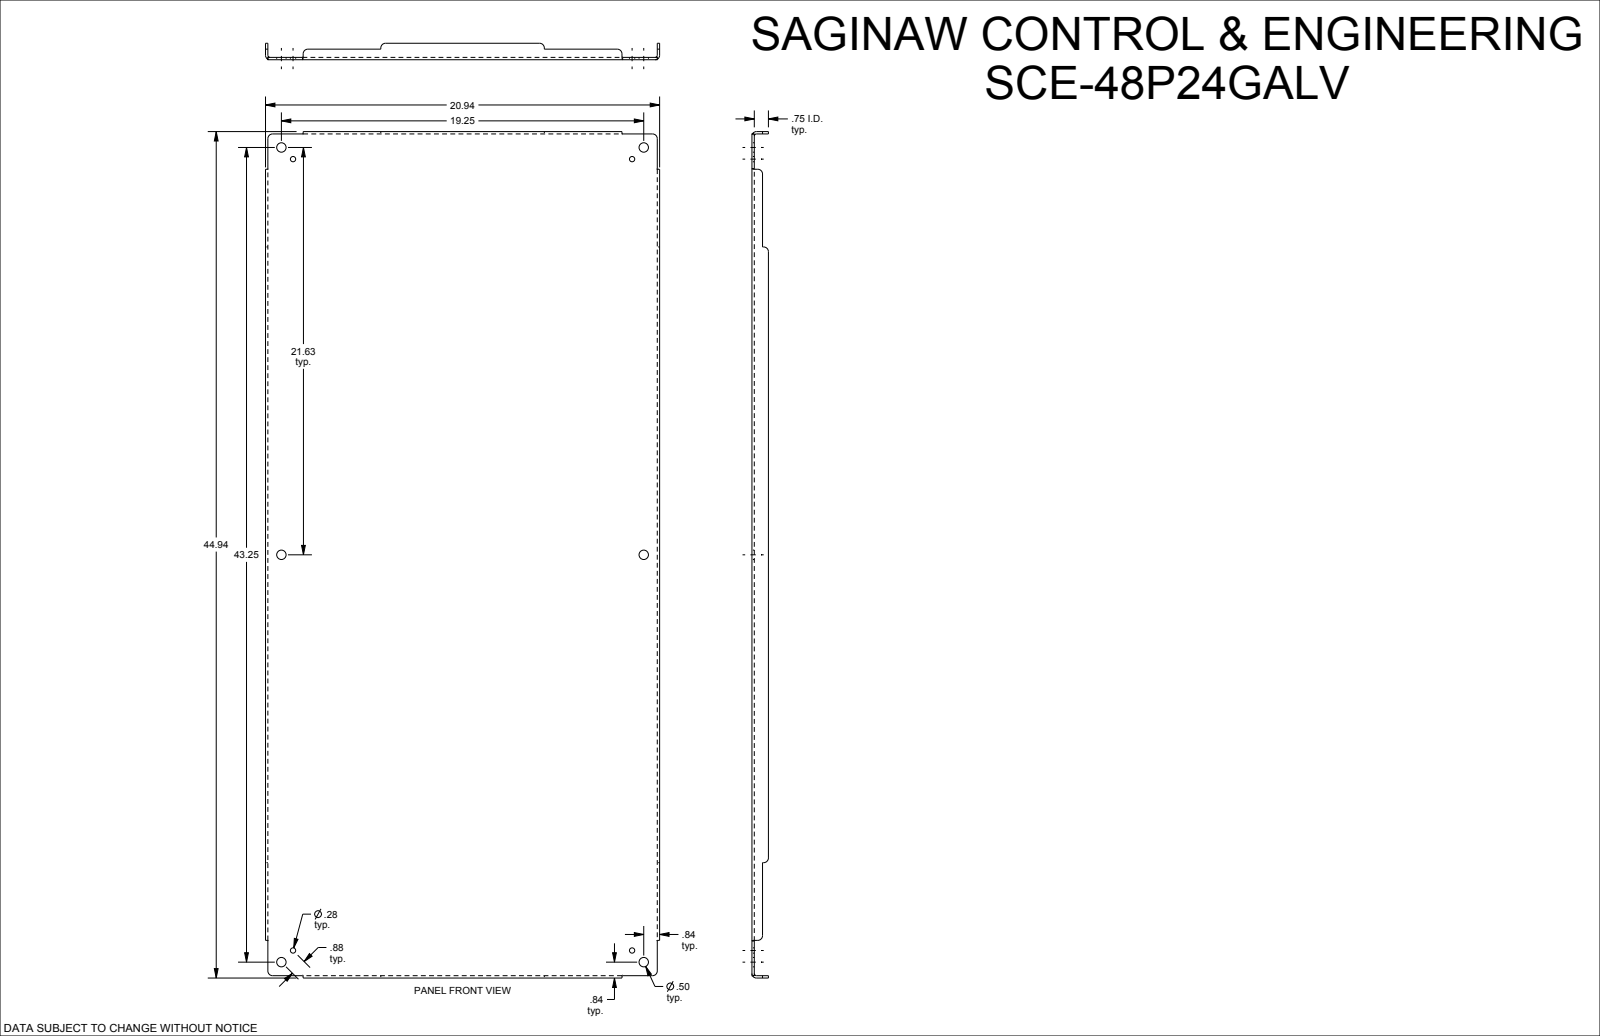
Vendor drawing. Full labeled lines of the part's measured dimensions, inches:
Part name (STEP PRODUCT): SCE-48P24GALV
STEP written by: SolidWorks 2019 (CONFIG_CONTROL_DESIGN)
Units: inches
Bodies: 1 solid, 108 faces (46 planar, 38 cylindrical, 24 other)
Overall size (bounding box): 44.938 × 20.938 × 0.875
Volume: 125.6 in³ · Surface area: 2 029 in²
Round holes (diameter × count): ⌀0.5 ×6, ⌀0.281 ×4
Partial cylindrical surfaces — rounded edges, fillets, slot ends (radius × count): R0.25 ×12, R0.112 ×4, R0.237 ×4
Main face-to-face distances: 0.125, 0.125, 20.813, 20.687, 20.938, 44.813, 0.75, 0.875, 44.687, 44.938
Hole centre spacings: 0.875, 18.641, 21.015, 21.625, 28.078, 28.951, 42.635, 46.524
